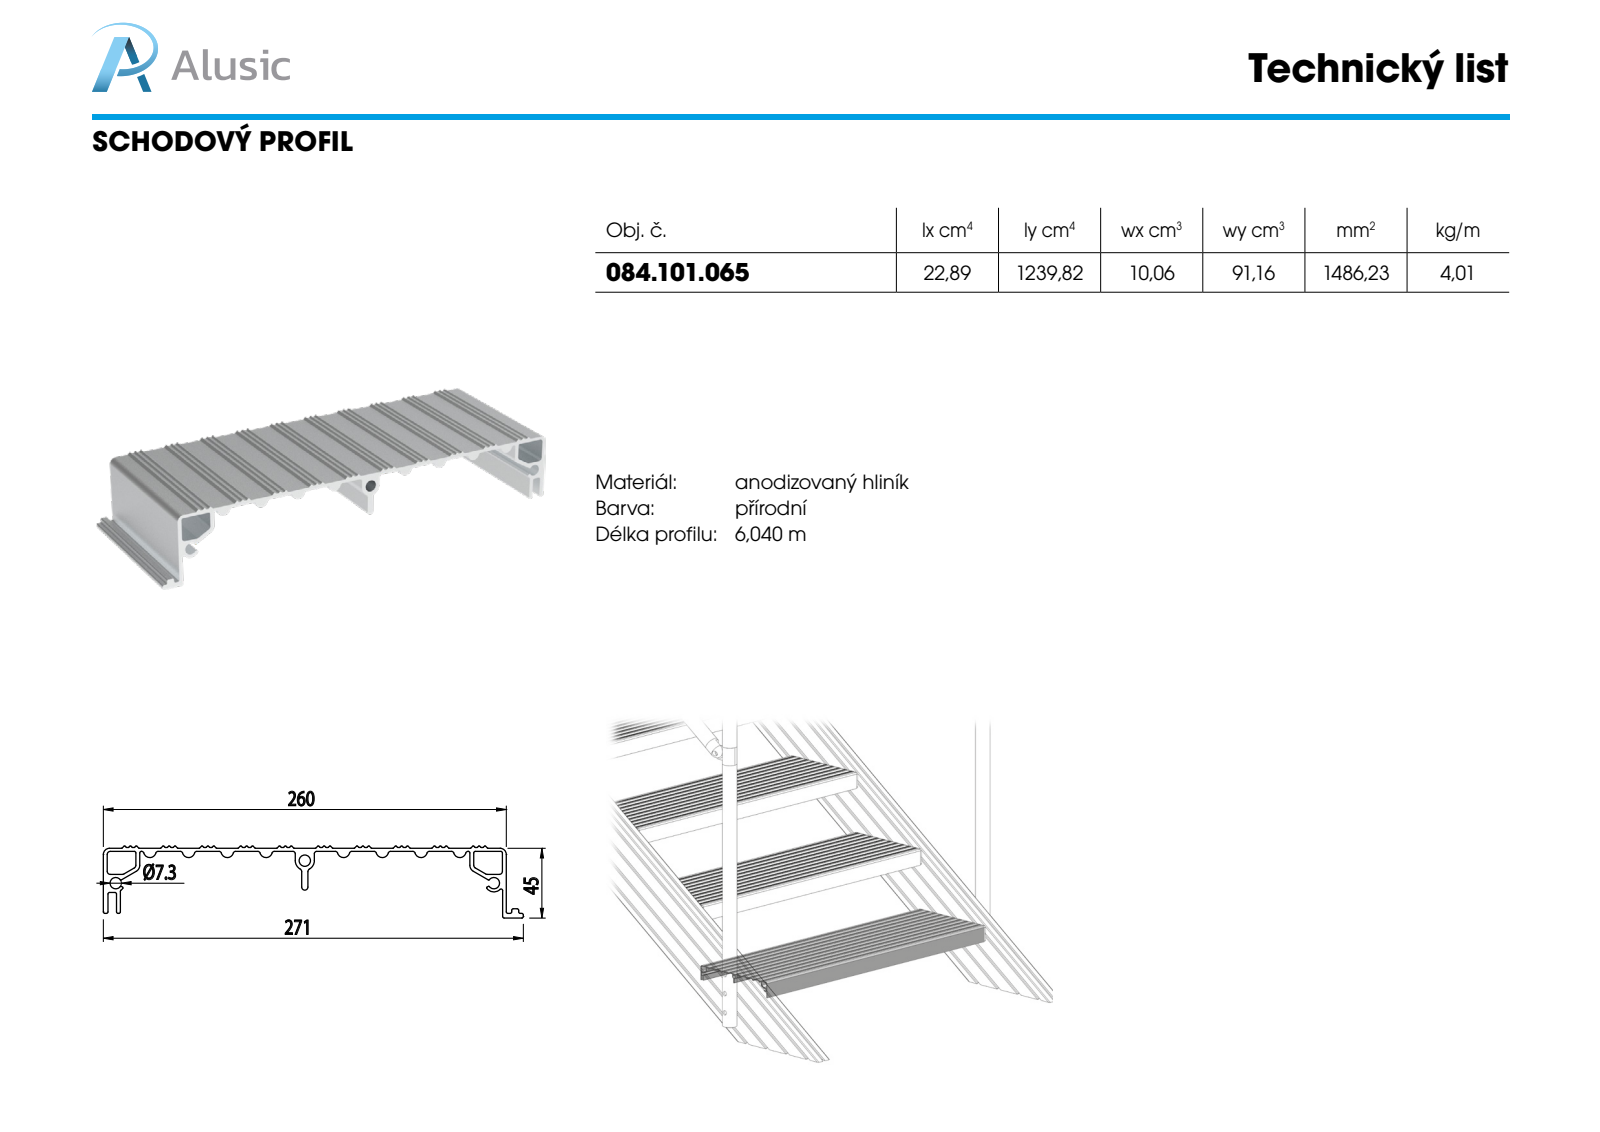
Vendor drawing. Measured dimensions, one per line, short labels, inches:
name: 084.101.065
written by: SolidWorks 2018 (AUTOMOTIVE_DESIGN)
unit: in
bodies: 1 solid, 341 faces (139 planar, 202 cylindrical, 0 other)
size: 10.669 × 3.937 × 1.831
volume: 9.07 in³; area: 159.6 in²
holes: 3× ⌀0.287
rounds: 96× R0.02, 21× R0.039, 18× R0.059, 10× R0.079, 10× R0.157, 2× R0.177, 2× R0.222, 1× R0.242
face distances: 0.079, 0.098, 1.392, 10.236, 0.827, 9.311, 0.02, 2.783, 9.803, 0.696
hole spacings: 4.837, 9.606
